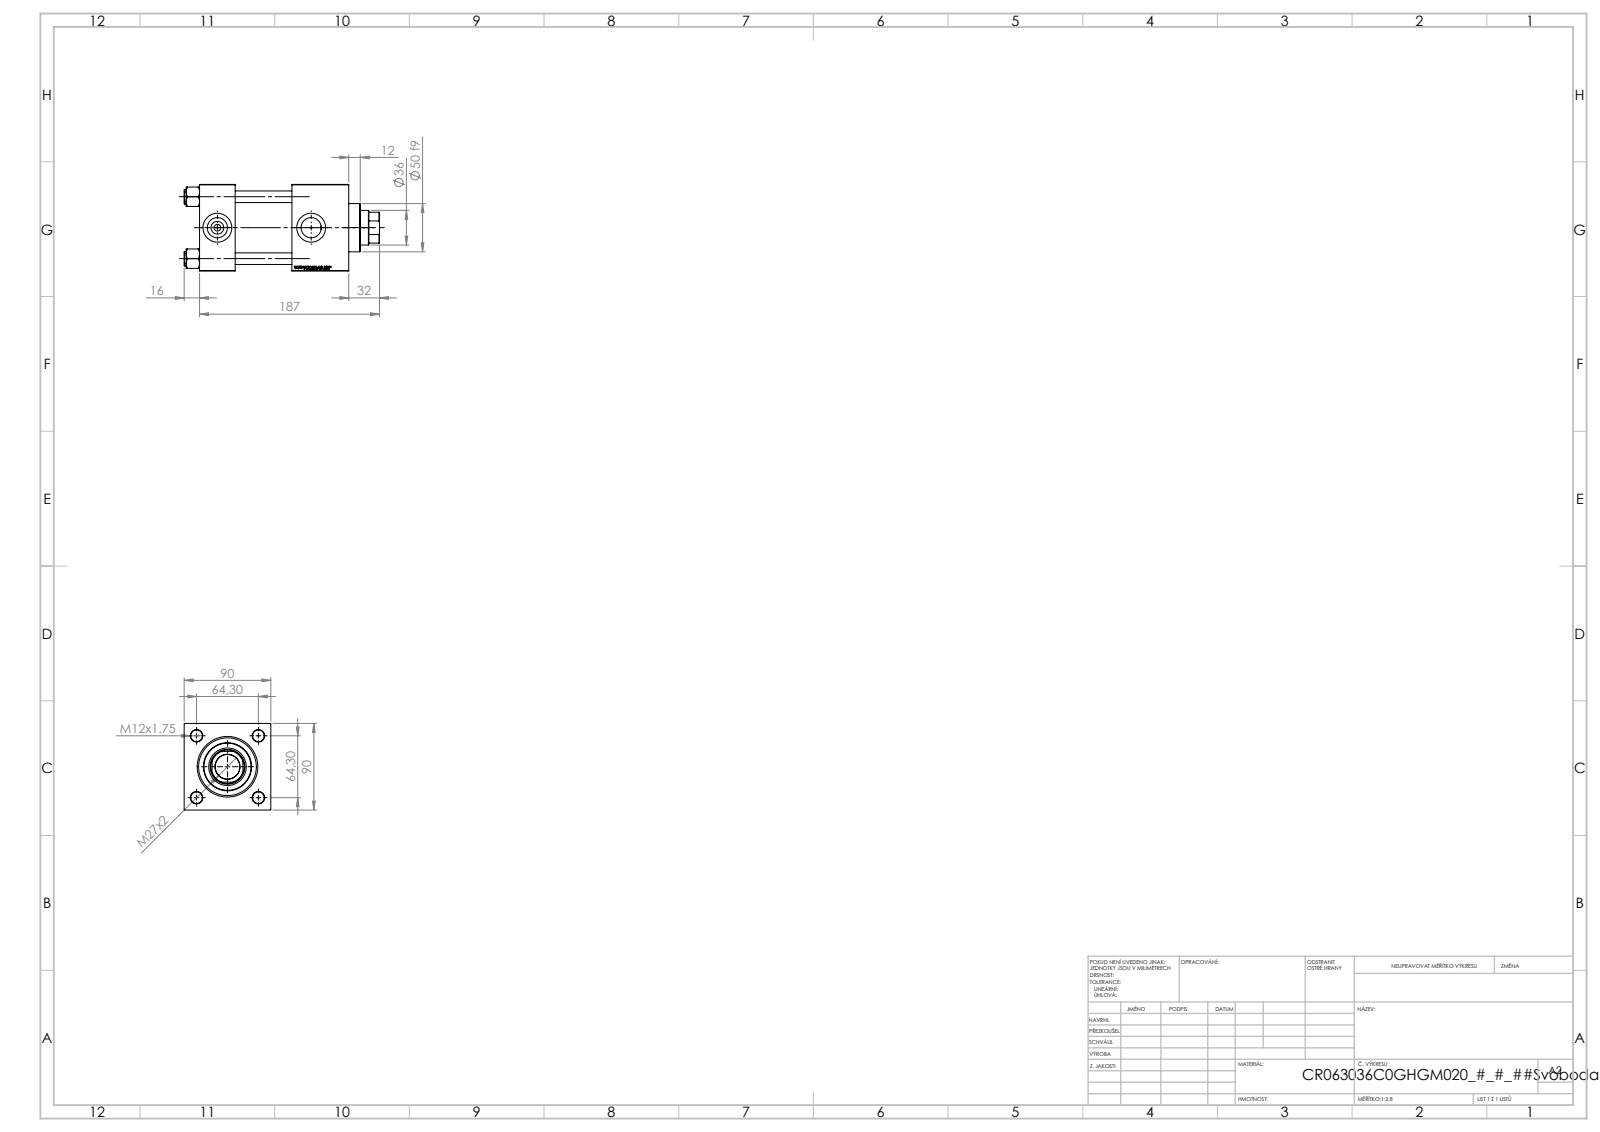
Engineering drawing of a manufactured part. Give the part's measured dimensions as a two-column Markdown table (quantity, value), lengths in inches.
| quantity | value |
| --- | --- |
| part name | V215CR_C_Body; V215_VC_A; V215CR_VCP_C; NUT_M5_C (+1 more) |
| STEP written by | SolidWorks 2019 (CONFIG_CONTROL_DESIGN) |
| units | inches |
| bodies | 11 solids, 1148 faces (526 planar, 86 cylindrical, 536 other) |
| overall size | 7.992 × 3.543 × 3.543 |
| volume | 59.07 in³ |
| surface area | 285.6 in² |
| round holes (diameter × count) | 0.472 × 4, 0.276 × 2, 0.825 × 2, 1.181 × 2, 1.004 × 1, 1.417 × 1, 1.535 × 1, 1.969 × 1, 2.362 × 1, 2.48 × 1 |
| round bosses / shafts (diameter × count) | 0.591 × 4, 2.717 × 1 |
| partial cylindrical surfaces (radius × count) | 0.689 × 1 |
| main face-to-face distances | 3.543, 2.323, 1.457, 6.102, 4.646, 3.78, 4.972, 3.516, 1.193, 1.13 |
| hole center spacings | 1.79, 2.531, 3.58, 3.839 |
